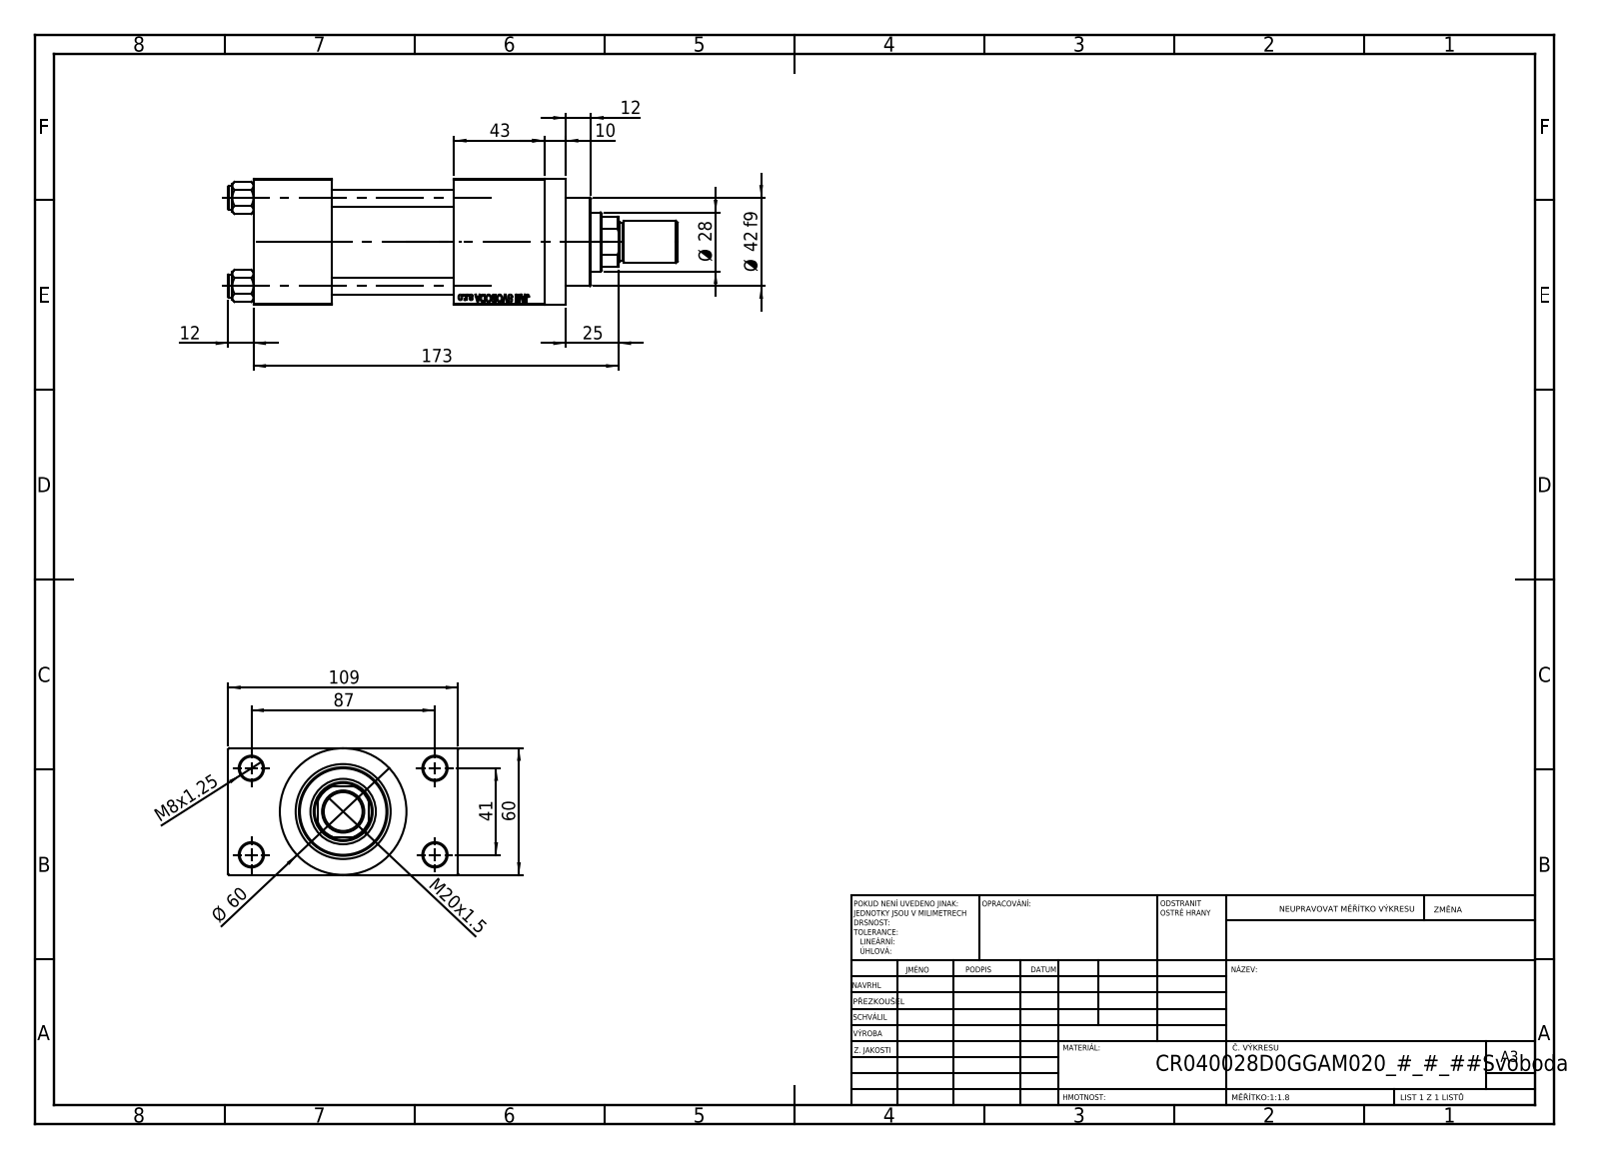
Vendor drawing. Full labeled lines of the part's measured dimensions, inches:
Part name (STEP PRODUCT): V215CR_D_TYCINKA; V215_VC_A; V215CR_D_Body; ROD_END_AH (+2 more)
STEP written by: SolidWorks 2019 (CONFIG_CONTROL_DESIGN)
Units: inches
Bodies: 12 solids, 1119 faces (502 planar, 93 cylindrical, 524 other)
Overall size (bounding box): 8.386 × 4.291 × 2.362
Volume: 33.12 in³ · Surface area: 201.9 in²
Round holes (diameter × count): ⌀0.315 ×4, ⌀0.433 ×4, ⌀0.276 ×2, ⌀0.656 ×2, ⌀0.945 ×2, ⌀0.728 ×1, ⌀1.102 ×1, ⌀1.22 ×1, ⌀1.575 ×1, ⌀1.772 ×1
Round bosses / shafts (diameter × count): ⌀0.433 ×4, ⌀2.362 ×1, ⌀1.811 ×1, ⌀1.654 ×1, ⌀0.787 ×1, ⌀0.709 ×1
Partial cylindrical surfaces — rounded edges, fillets, slot ends (radius × count): R0.531 ×1
Main face-to-face distances: 2.362, 3.327, 0.965, 2.283, 1.457, 3.74, 5.433, 3.976, 1.693, 4.291
Hole centre spacings: 0.892, 1.161, 1.642, 1.856, 1.893, 2.533, 3.011, 1.614
